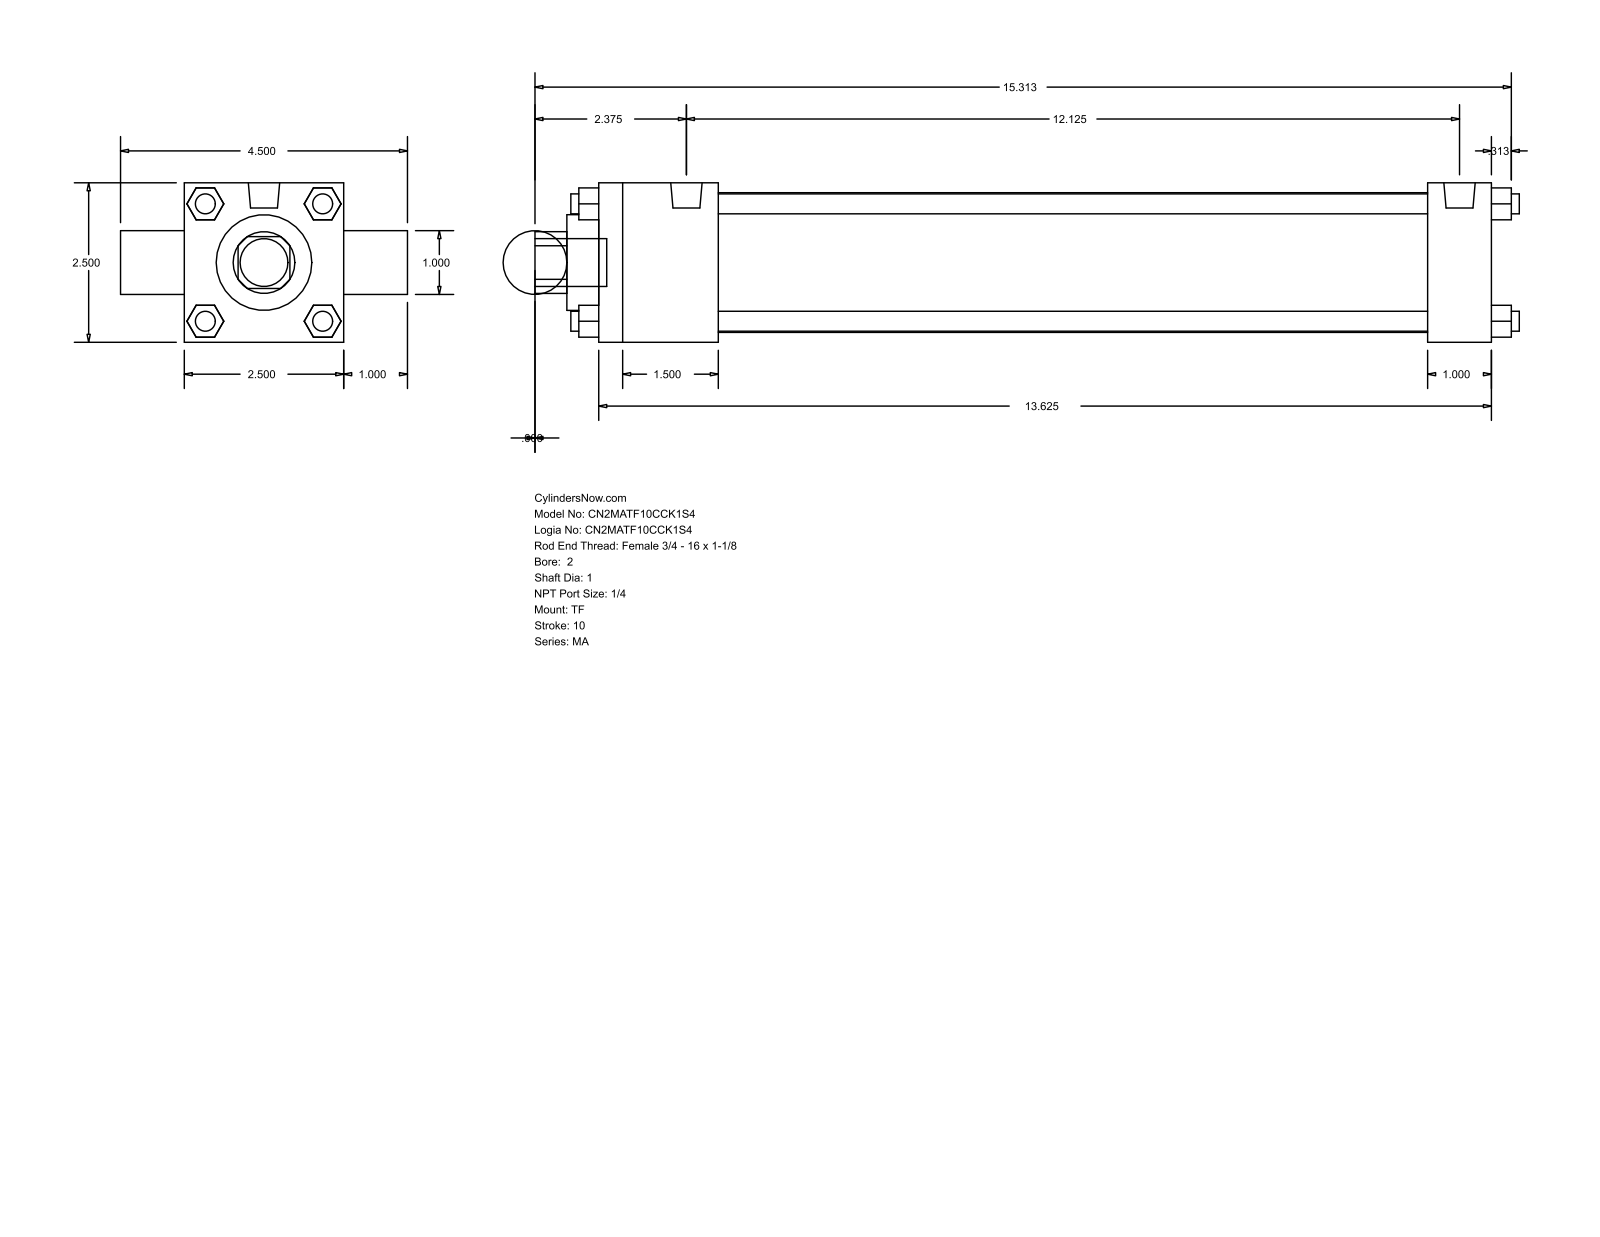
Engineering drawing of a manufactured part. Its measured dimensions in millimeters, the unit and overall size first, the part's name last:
Units: millimetres
Overall size (bounding box): 392.11 × 114.3 × 63.5
Round holes (diameter × count): ⌀25.4 ×2, ⌀38.1 ×1, ⌀55.63 ×1
Round bosses / shafts (diameter × count): ⌀7.94 ×7, ⌀12.49 ×2, ⌀19.05 ×1
Partial cylindrical surfaces — rounded edges, fillets, slot ends (radius × count): R12.29 ×1
Main face-to-face distances: 63.5, 25.4, 355.6, 12.7, 47.63, 330.2, 282.57, 307.97, 88.9, 40.47
Bodies: 0 solids, 120 faces (92 planar, 28 cylindrical, 0 other)
Part name (STEP PRODUCT): MA_TF__0200_1
STEP written by: GSSL Pune (CONFIG_CONTROL_DESIGN)
